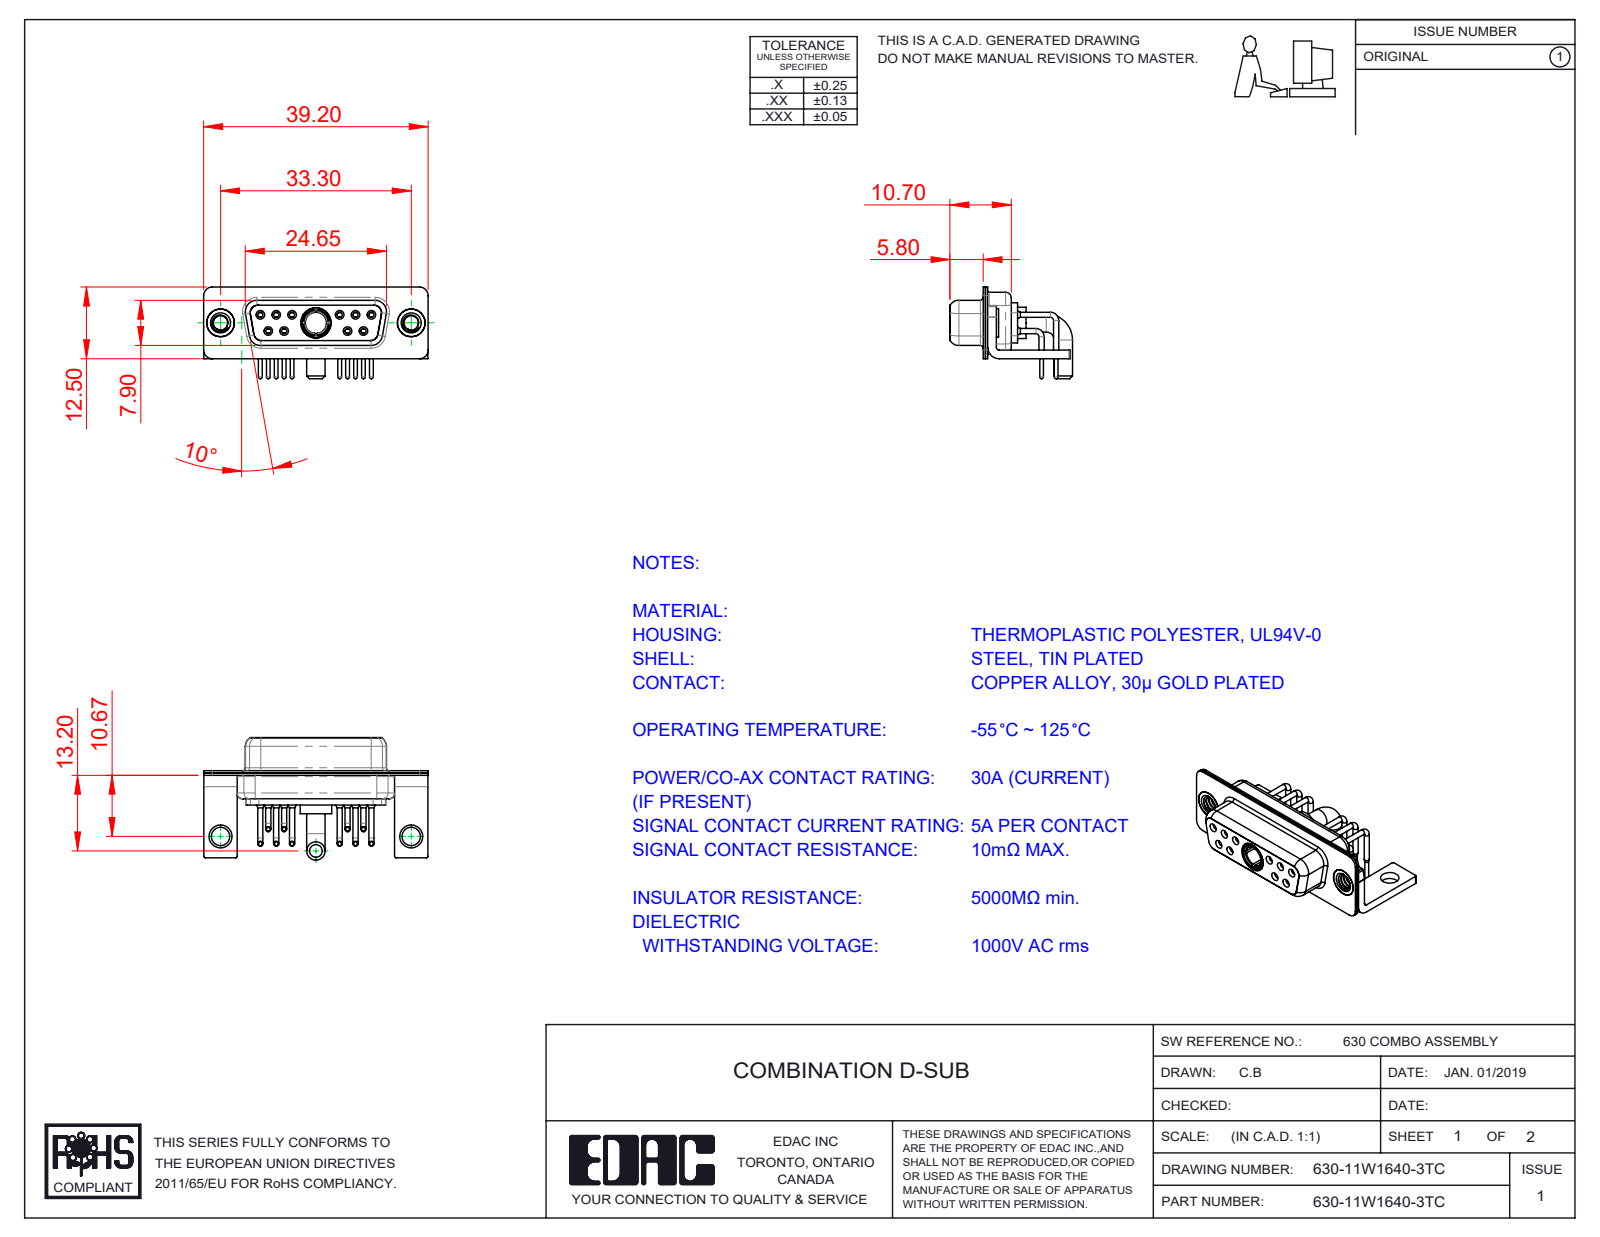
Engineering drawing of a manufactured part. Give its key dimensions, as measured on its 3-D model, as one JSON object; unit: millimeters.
{"part_name": "630Combo Threaded Rivet_B; 630-11W1640-3TC; 630Combo Shell Rear_15 Contacts; 630Combo Shell Front_15 Contacts (+5 more)", "step_written_by": "SolidWorks 2020 (CONFIG_CONTROL_DESIGN)", "units": "millimeters", "bodies": {"solids": 19, "faces": 925, "planar": 266, "cylindrical": 410, "other": 249}, "overall_size": [39.2, 21.4, 16], "volume_mm3": 2936, "surface_area_mm2": 6878, "round_holes": [[0.9, 10], [1.1, 10], [1.5, 10], [2, 10], [1.7, 6], [1.6, 4], [4.85, 3], [2.5, 2], [3.2, 2], [4, 2], [4.05, 2], [3.7, 1]], "round_bosses_or_shafts": [[0.9, 10], [0.65, 10], [1.6, 6], [5, 2], [4.95, 2], [4.8, 2], [3.2, 2], [5.5, 1]], "partial_cylinders_radius": [[0.25, 16], [1.5, 16], [2, 13], [1.35, 12], [1.6, 8], [0.5, 5], [0.6, 4], [0.65, 4]], "face_to_face_distances": [0.4, 0.8, 1.4, 0.45, 8.45, 1.5, 1.8, 8.9, 6.2, 2.3], "hole_center_spacings": [3.16, 2.77, 13.85, 11.08, 16.62, 5.03, 5.04, 5.54]}
